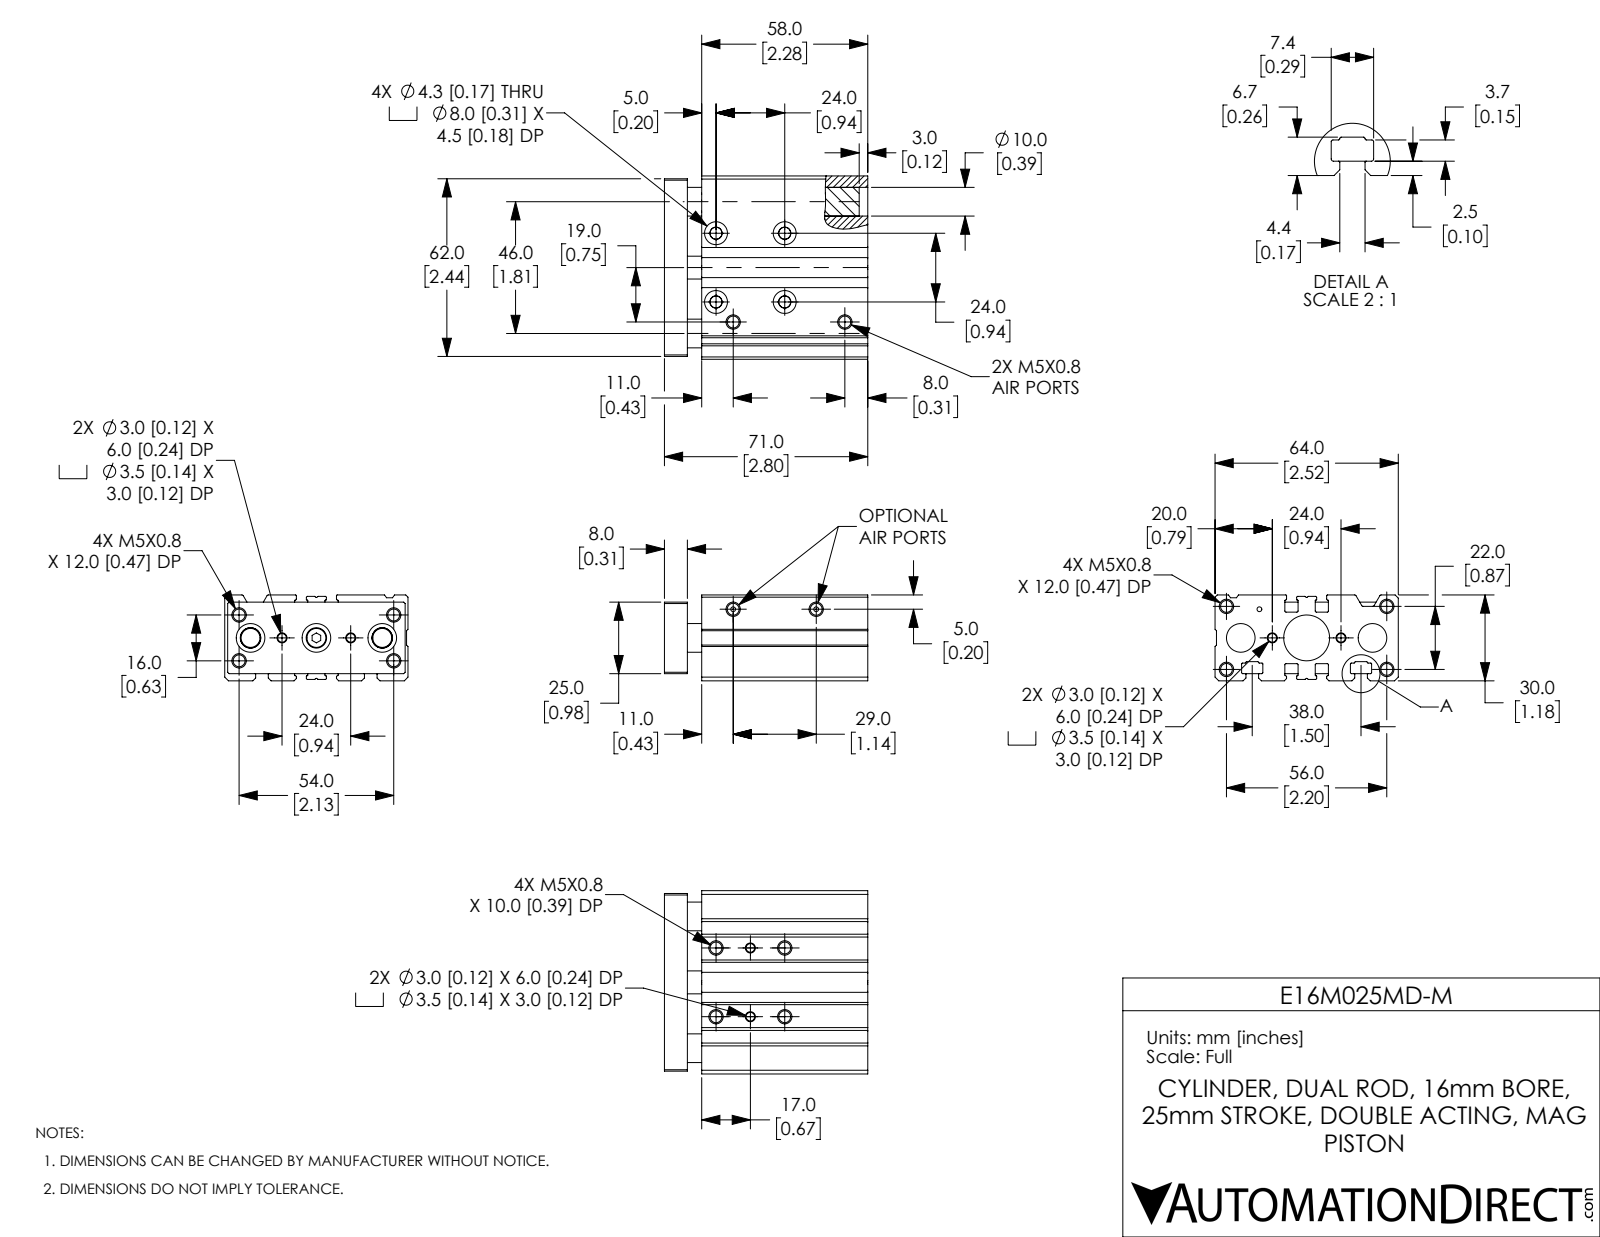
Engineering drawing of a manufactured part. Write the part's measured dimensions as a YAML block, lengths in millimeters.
part_name: "E16M025MD-M; E16M025MD-M_BODY; E16M025MD-M_ENDPLATE"
step_written_by: "SolidWorks 2019 (CONFIG_CONTROL_DESIGN)"
units: millimeters
bodies: {solids: 5, faces: 411, planar: 133, cylindrical: 192, other: 86}
overall_size: [71, 64, 30]
volume: 102489
surface_area: 41286
round_holes:
  - {diameter: 4.13, count: 16}
  - {diameter: 3, count: 4}
  - {diameter: 3.5, count: 4}
  - {diameter: 4.3, count: 4}
  - {diameter: 8, count: 4}
  - {diameter: 1.67, count: 3}
  - {diameter: 5, count: 3}
  - {diameter: 10, count: 3}
  - {diameter: 7.11, count: 2}
  - {diameter: 10, count: 1}
  - {diameter: 16, count: 1}
  - {diameter: 16, count: 1}
round_bosses_or_shafts:
  - {diameter: 8, count: 1}
  - {diameter: 7.11, count: 1}
partial_cylinders:
  - {radius: 0.2, count: 22}
  - {radius: 0.4, count: 20}
  - {radius: 0.25, count: 8}
  - {radius: 0.3, count: 6}
  - {radius: 0.5, count: 4}
face_to_face_distances: [63, 30, 0.5, 27.5, 64, 3.5, 5, 13, 6, 4]
hole_center_spacings: [12, 24, 3.16, 8.94, 12.08, 17, 19.03, 19.42]
